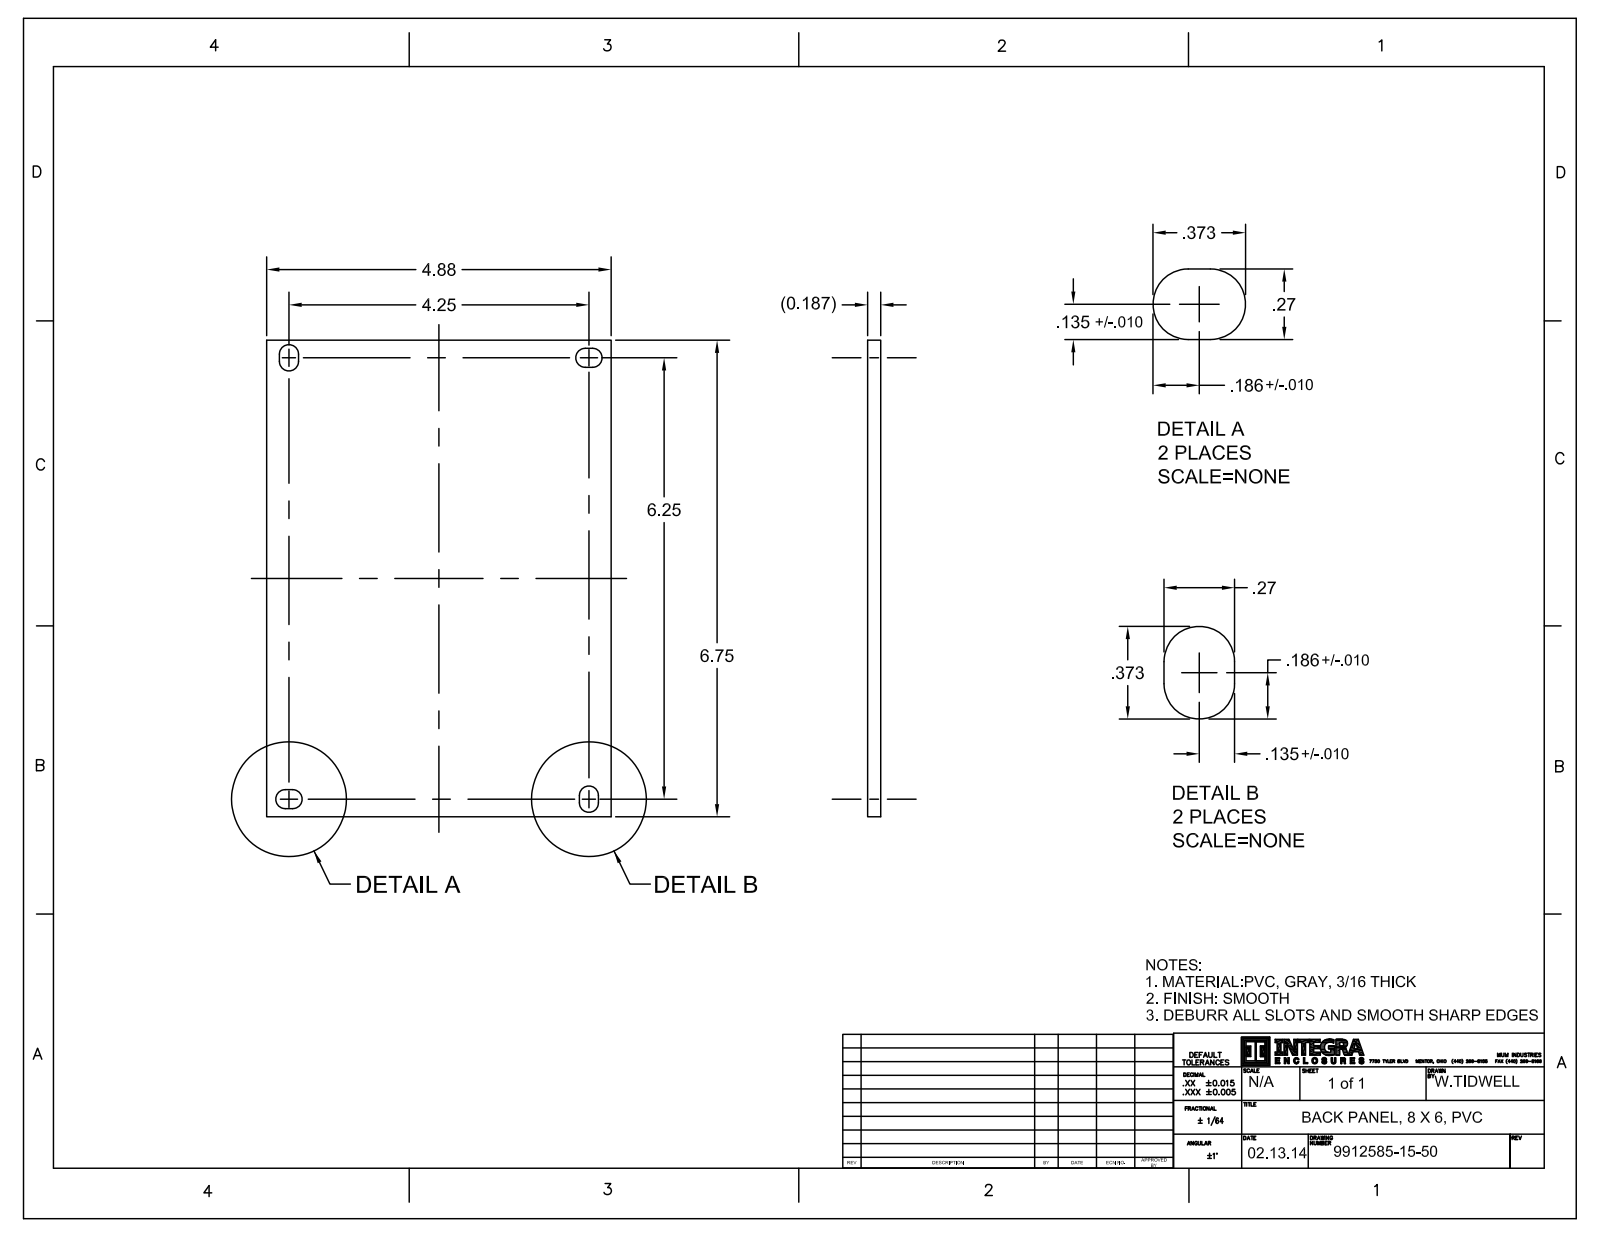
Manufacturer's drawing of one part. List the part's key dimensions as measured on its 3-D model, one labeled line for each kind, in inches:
Part name (STEP PRODUCT): 9912585-15-50; 9912537-82-10; PVCBP86_ASM
STEP written by: CREO PARAMETRIC BY PTC INC, 2016050 (CONFIG_CONTROL_DESIGN)
Units: inches
Bodies: 5 solids, 514 faces (90 planar, 336 cylindrical, 88 other)
Overall size (bounding box): 6.75 × 4.88 × 0.63
Volume: 6.201 in³ · Surface area: 73.57 in²
Round bosses / shafts (diameter × count): ⌀0.373 ×4, ⌀0.19 ×4, ⌀0.149 ×4
Partial cylindrical surfaces — rounded edges, fillets, slot ends (radius × count): R0.125 ×8
Main face-to-face distances: 0.187, 4.88, 6.75, 0.25, 0.313, 0.5, 0.125, 0.375, 6.375, 6.625
